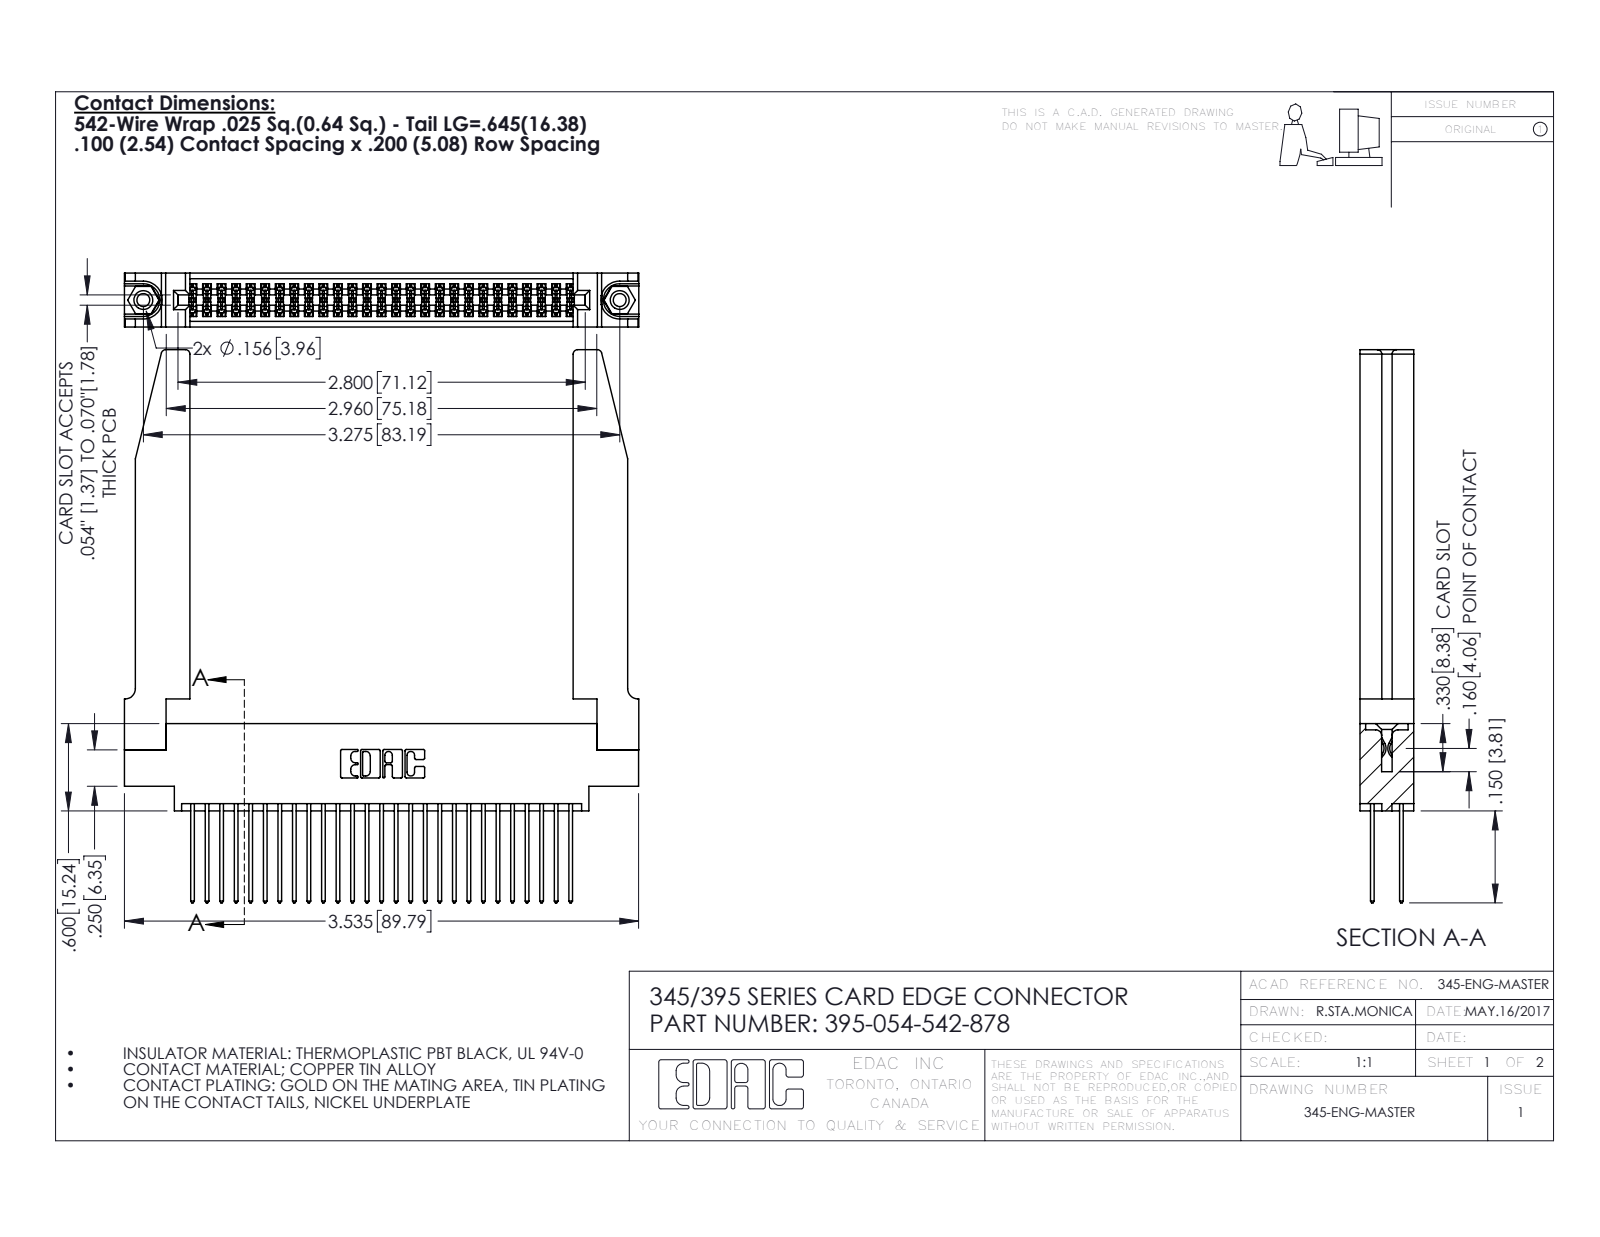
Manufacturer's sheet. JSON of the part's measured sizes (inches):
{"part_name": "345-292-001_345-293-142; 395-054-542-878; 345-250-001_345-250-001-102; 345-220-078_345-220-078 (+1 more)", "step_written_by": "SolidWorks 2016 (CONFIG_CONTROL_DESIGN)", "units": "inches", "bodies": {"solids": 59, "faces": 3064, "planar": 2008, "cylindrical": 1004, "other": 52}, "overall_size": [3.802, 3.536, 0.37], "volume_in3": 1.007, "surface_area_in2": 32.18, "round_holes": [[0.089, 2], [0.125, 2], [0.156, 2], [0.064, 1]], "round_bosses_or_shafts": [[0.155, 2]], "partial_cylinders_radius": [[0.006, 81], [0.01, 54], [0.01, 22], [0.03, 8], [0.007, 6], [0.031, 6], [0.026, 3], [0.014, 2]], "face_to_face_distances": [0.37, 0.072, 0.298, 0.098, 0.272, 0.025, 0.2, 0.225, 0.175, 0.148], "hole_center_spacings": [0.27, 3.04, 3.275]}
